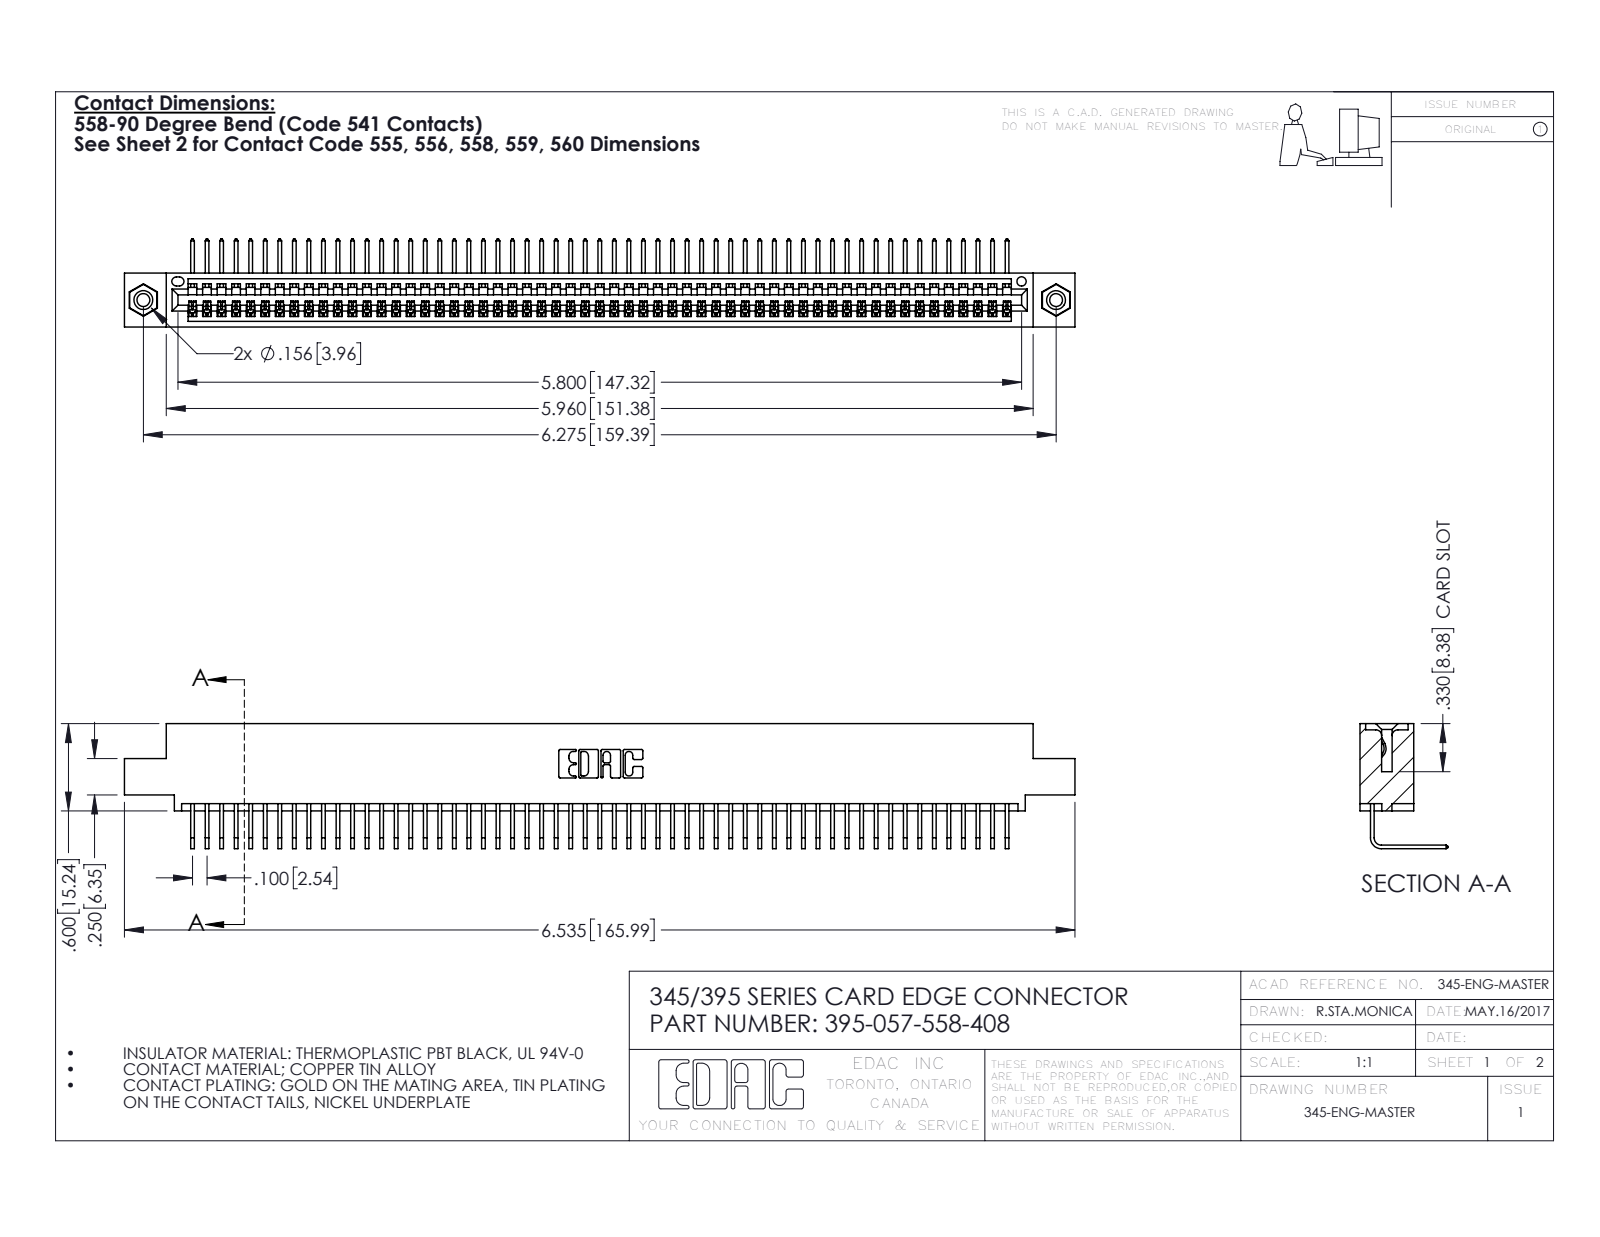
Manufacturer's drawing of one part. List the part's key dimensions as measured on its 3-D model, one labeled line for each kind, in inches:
Part name (STEP PRODUCT): 345 Part_0.110 Offset - 0.156 Dia-TI; 345-250-001_345-250-003-102; 345-292-001_558 Tail - 2; 395-057-558-408
STEP written by: SolidWorks 2016 (CONFIG_CONTROL_DESIGN)
Units: inches
Bodies: 60 solids, 3610 faces (2510 planar, 1084 cylindrical, 16 other)
Overall size (bounding box): 6.535 × 0.859 × 0.605
Volume: 0.976 in³ · Surface area: 35.16 in²
Round holes (diameter × count): ⌀0.089 ×2, ⌀0.125 ×2, ⌀0.156 ×2, ⌀0.064 ×1
Round bosses / shafts (diameter × count): ⌀0.155 ×2
Partial cylindrical surfaces — rounded edges, fillets, slot ends (radius × count): R0.006 ×114, R0.01 ×22, R0.007 ×6, R0.031 ×6, R0.026 ×3, R0.031 ×2, R0.04 ×2, R0.014 ×1
Main face-to-face distances: 0.072, 0.298, 0.37, 0.2, 0.098, 0.272, 0.025, 0.225, 0.149, 0.072
Hole centre spacings: 0.27, 6.039, 6.275
